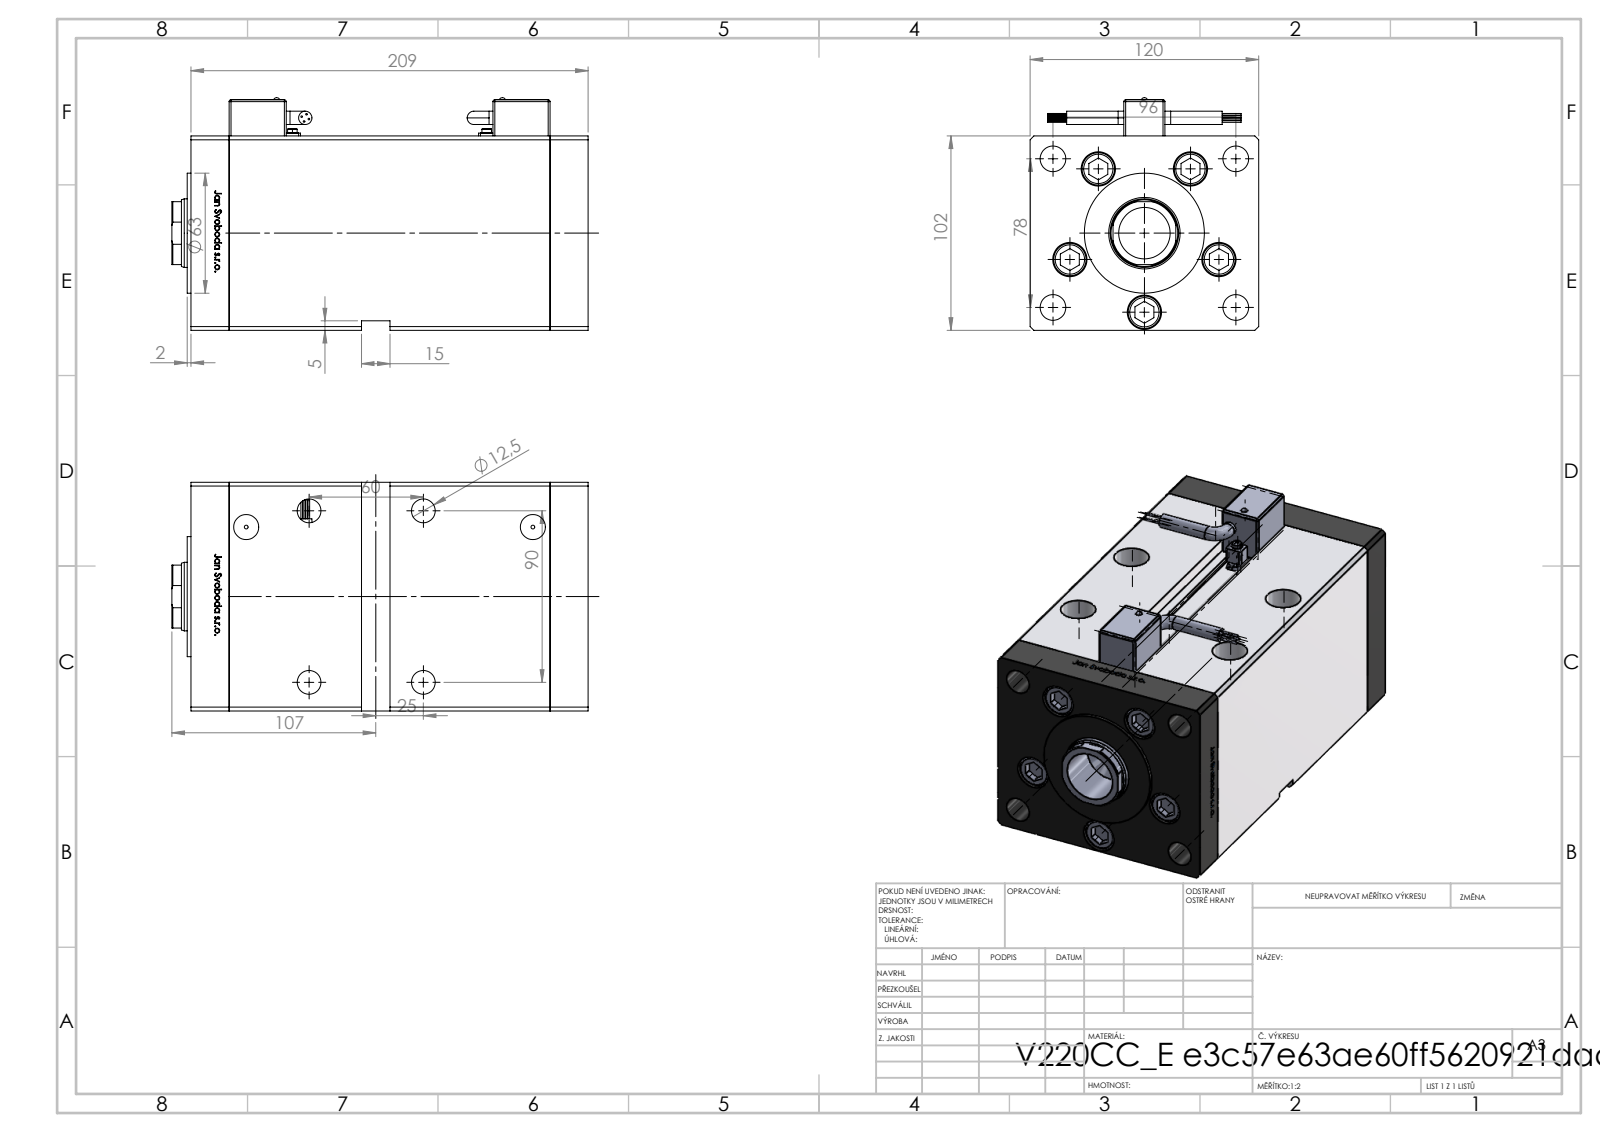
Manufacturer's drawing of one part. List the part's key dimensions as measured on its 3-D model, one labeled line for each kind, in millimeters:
Part name (STEP PRODUCT): V220C_FRONT_E; ALLEN BOLT; V220C BACK_E; V220C_E_VC (+2 more)
STEP written by: SolidWorks 2019 (CONFIG_CONTROL_DESIGN)
Units: millimetres
Bodies: 16 solids, 1410 faces (551 planar, 251 cylindrical, 608 other)
Overall size (bounding box): 218.5 × 122.1 × 120
Volume: 2 214 000 mm³ · Surface area: 294 340 mm²
Round holes (diameter × count): ⌀13.5 ×9, ⌀18 ×5, ⌀12.5 ×4, ⌀18.5 ×4, ⌀2 ×2, ⌀3.6 ×2, ⌀5 ×2, ⌀7 ×2, ⌀13.16 ×2, ⌀27 ×1, ⌀36 ×1, ⌀37.5 ×1
Round bosses / shafts (diameter × count): ⌀0.85 ×8, ⌀17 ×5, ⌀8 ×5, ⌀7 ×4, ⌀6 ×2, ⌀3.5 ×2, ⌀2.5 ×2, ⌀63 ×1
Partial cylindrical surfaces — rounded edges, fillets, slot ends (radius × count): R1 ×24, R4 ×4, R0.93 ×2, R17.5 ×1
Main face-to-face distances: 120, 102, 168.5, 20, 188.5, 208.5, 11, 95.5, 6.5, 70.8
Hole centre spacings: 41.5, 61.85, 8.25, 24.39, 26.69, 39.85, 43.82, 45.84
